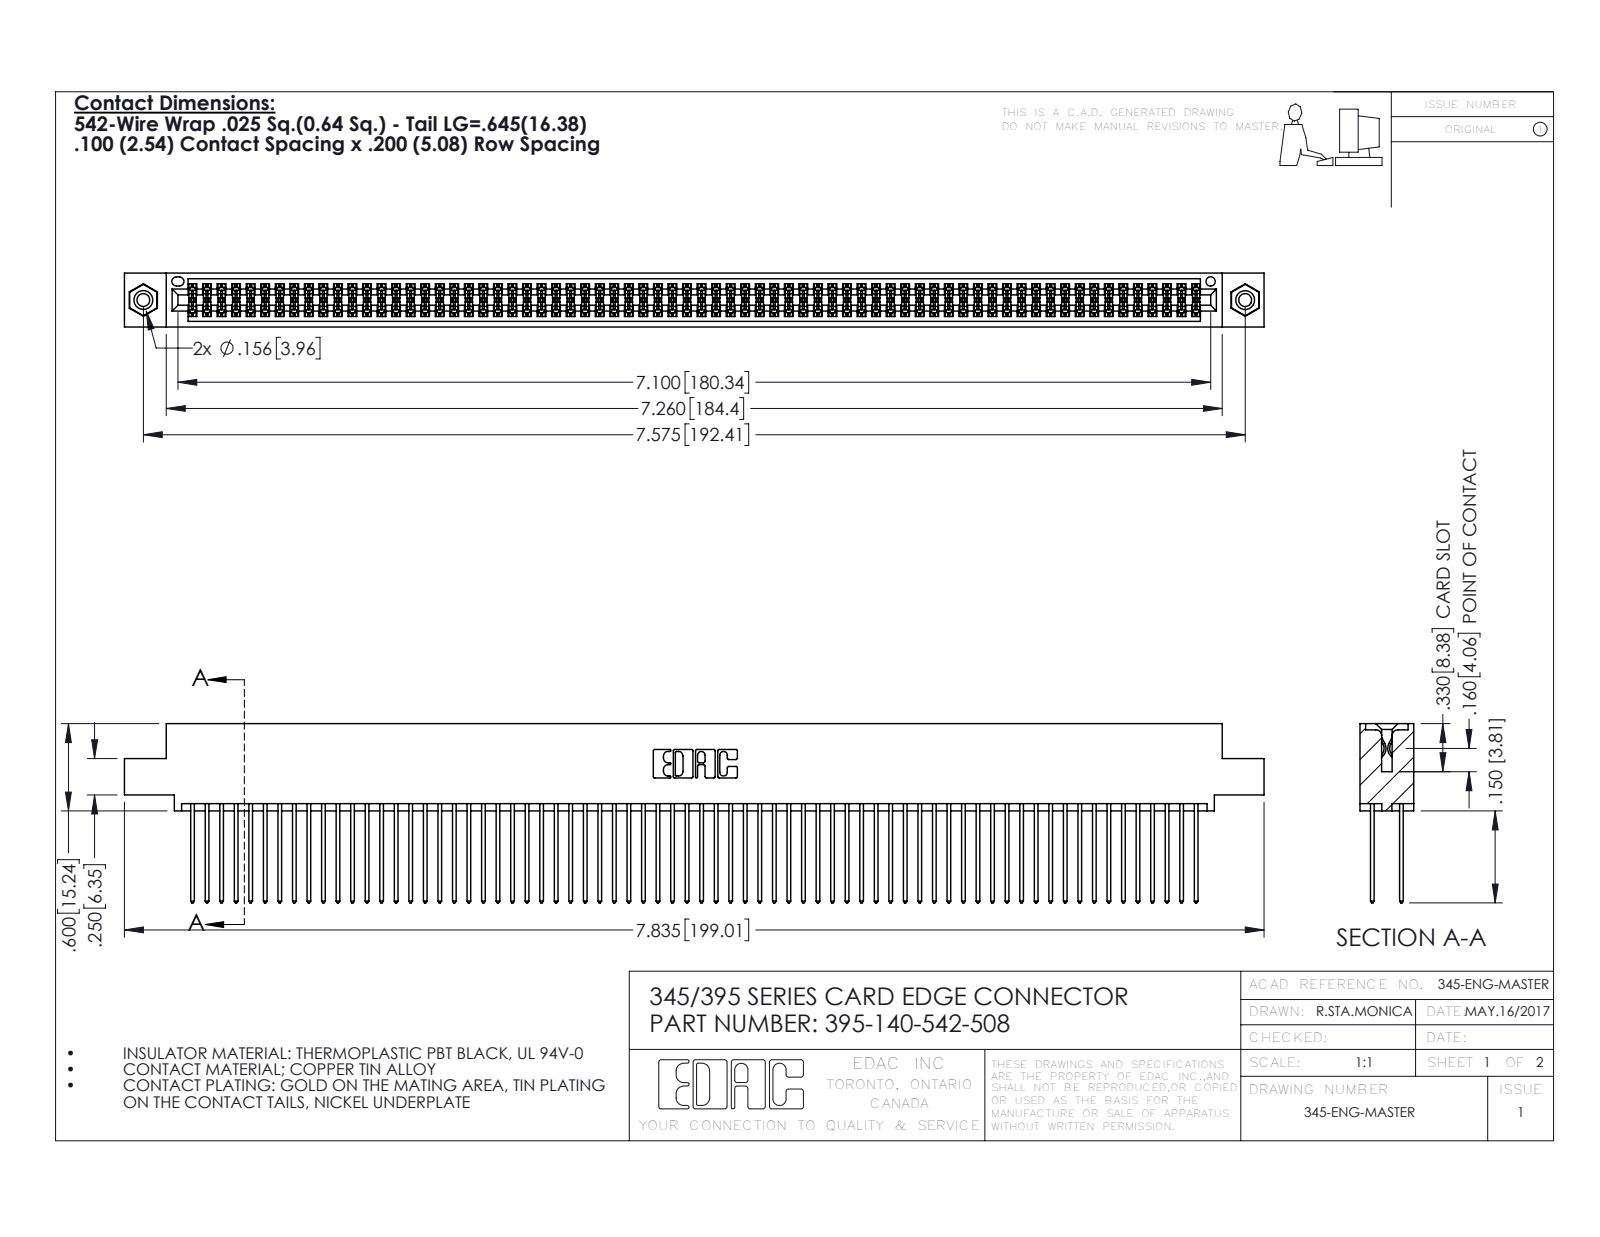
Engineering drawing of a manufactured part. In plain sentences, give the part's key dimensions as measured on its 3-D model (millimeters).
The part is named "345 Part_0.110 Offset - 0.156 Dia-TI; 345-250-001_345-250-003-102; 395-140-542-508; 345-292-001_345-293-142". Its 3-D file was written by "SolidWorks 2016 (CONFIG_CONTROL_DESIGN)". It is 143 solids with 7190 faces: 4736 planar, 2438 cylindrical and 16 other. Overall it measures 199 by 31.3 by 9.4 millimeters. Its volume is 20 170 cubic millimeters and its surface area 33 500 square millimeters. Round holes: 2 of diameter 2.3, 2 of diameter 3.2, 2 of diameter 4, 1 of diameter 1.6. Round bosses or shafts: 2 of diameter 3.9. Partial cylindrical surfaces (rounded edges, fillets, slot ends): 210 of radius 0.2, 140 of radius 0.3, 22 of radius 0.3, 6 of radius 0.2, 6 of radius 0.8, 3 of radius 0.7, 2 of radius 0.4, 2 of radius 0.5. The main face-to-face distances are 1.8, 7.6, 5.1, 2.5, 6.9, 0.6, 5.7, 9.4, 4.4, 3.8. The hole center spacings are 6.9, 186.4, 192.4.
